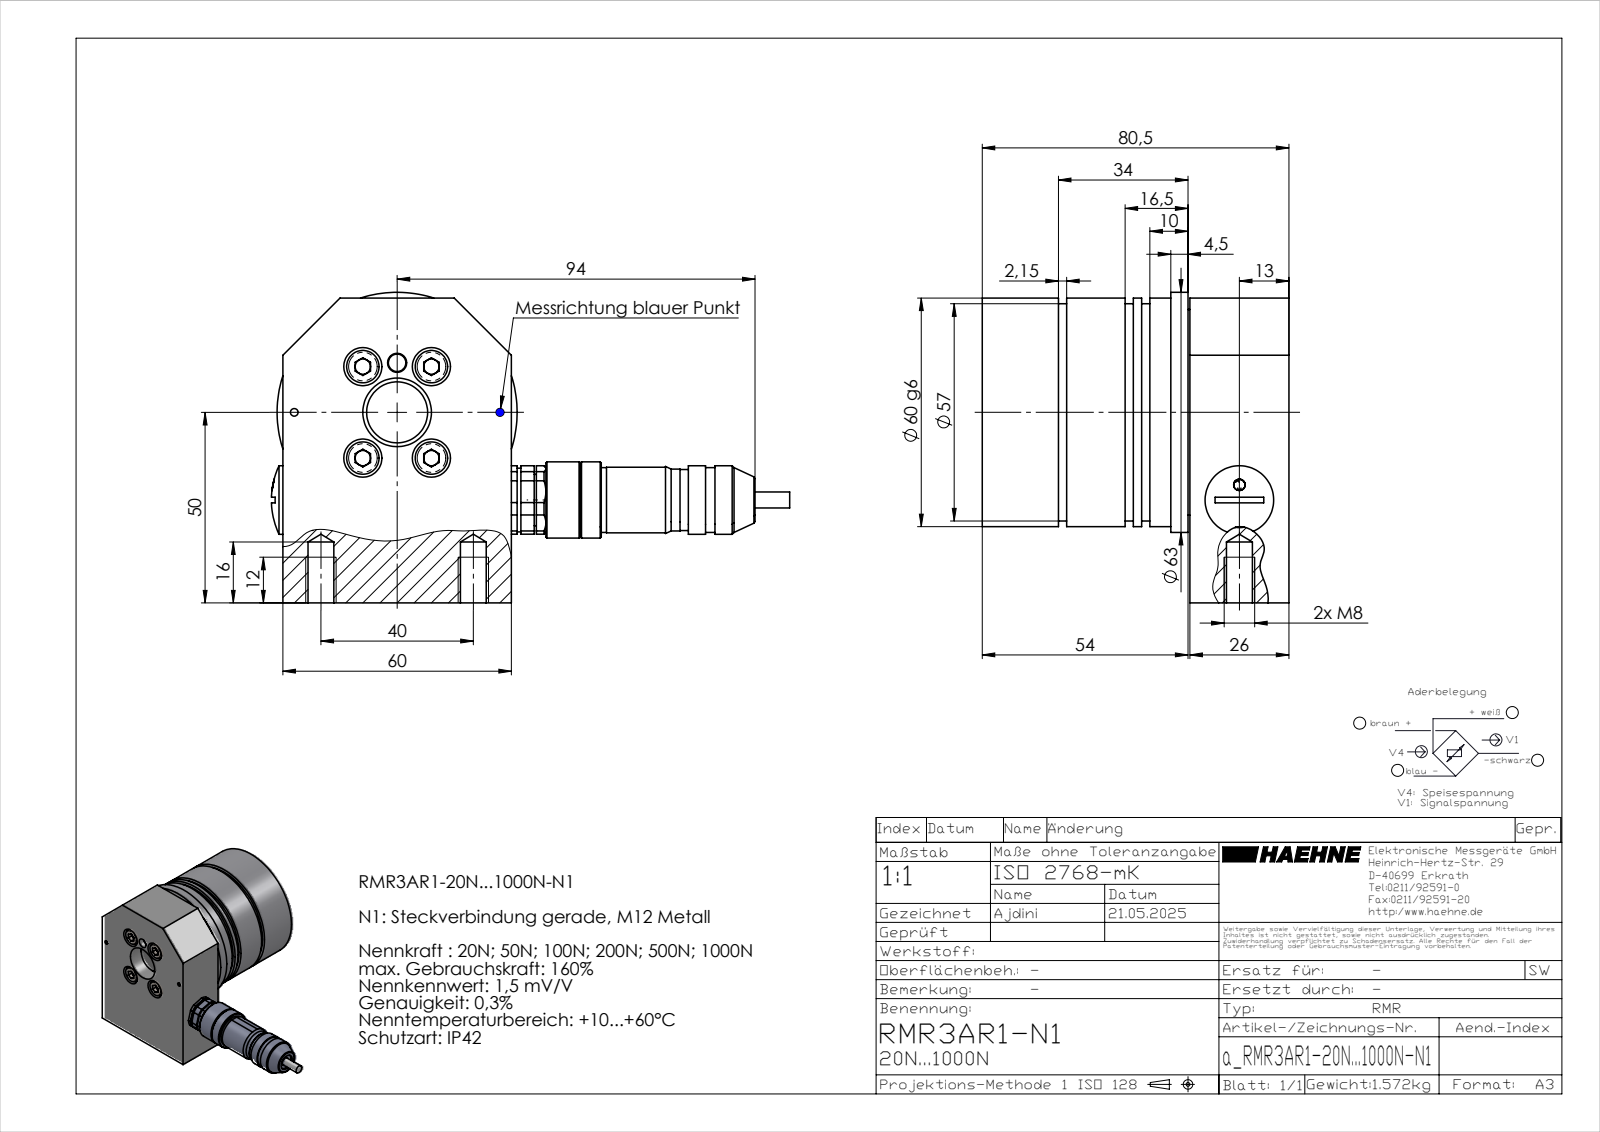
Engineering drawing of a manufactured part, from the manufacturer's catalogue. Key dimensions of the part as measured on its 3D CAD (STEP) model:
Part name (STEP PRODUCT): a_RMR3AR1-20N...1000N-N1
STEP written by: SolidWorks 2023 (AUTOMOTIVE_DESIGN)
Units: millimetres
Bodies: 16 solids, 491 faces (248 planar, 156 cylindrical, 87 other)
Overall size (bounding box): 136.04 × 81.5 × 80.5
Volume: 243 343 mm³ · Surface area: 74 838 mm²
Round holes (diameter × count): ⌀1 ×5, ⌀4.2 ×4, ⌀5.3 ×4, ⌀10 ×4, ⌀2 ×2, ⌀6.8 ×2, ⌀0.64 ×1, ⌀3 ×1, ⌀4.5 ×1, ⌀5 ×1, ⌀8.2 ×1, ⌀8.37 ×1
Round bosses / shafts (diameter × count): ⌀0.86 ×5, ⌀8.5 ×4, ⌀5 ×4, ⌀1.5 ×4, ⌀1 ×4, ⌀63 ×1, ⌀60 ×1, ⌀57 ×1
Partial cylindrical surfaces — rounded edges, fillets, slot ends (radius × count): R0.3 ×6, R1 ×4, R0.57 ×1, R0.6 ×1, R0.77 ×1, R3.5 ×1, R24 ×1, R40 ×1
Main face-to-face distances: 11.5, 48.5, 37, 73, 54.5, 62, 11, 47, 15, 26
Hole centre spacings: 2.5, 3.54, 15, 21.63, 37.95, 5, 9.06, 18
